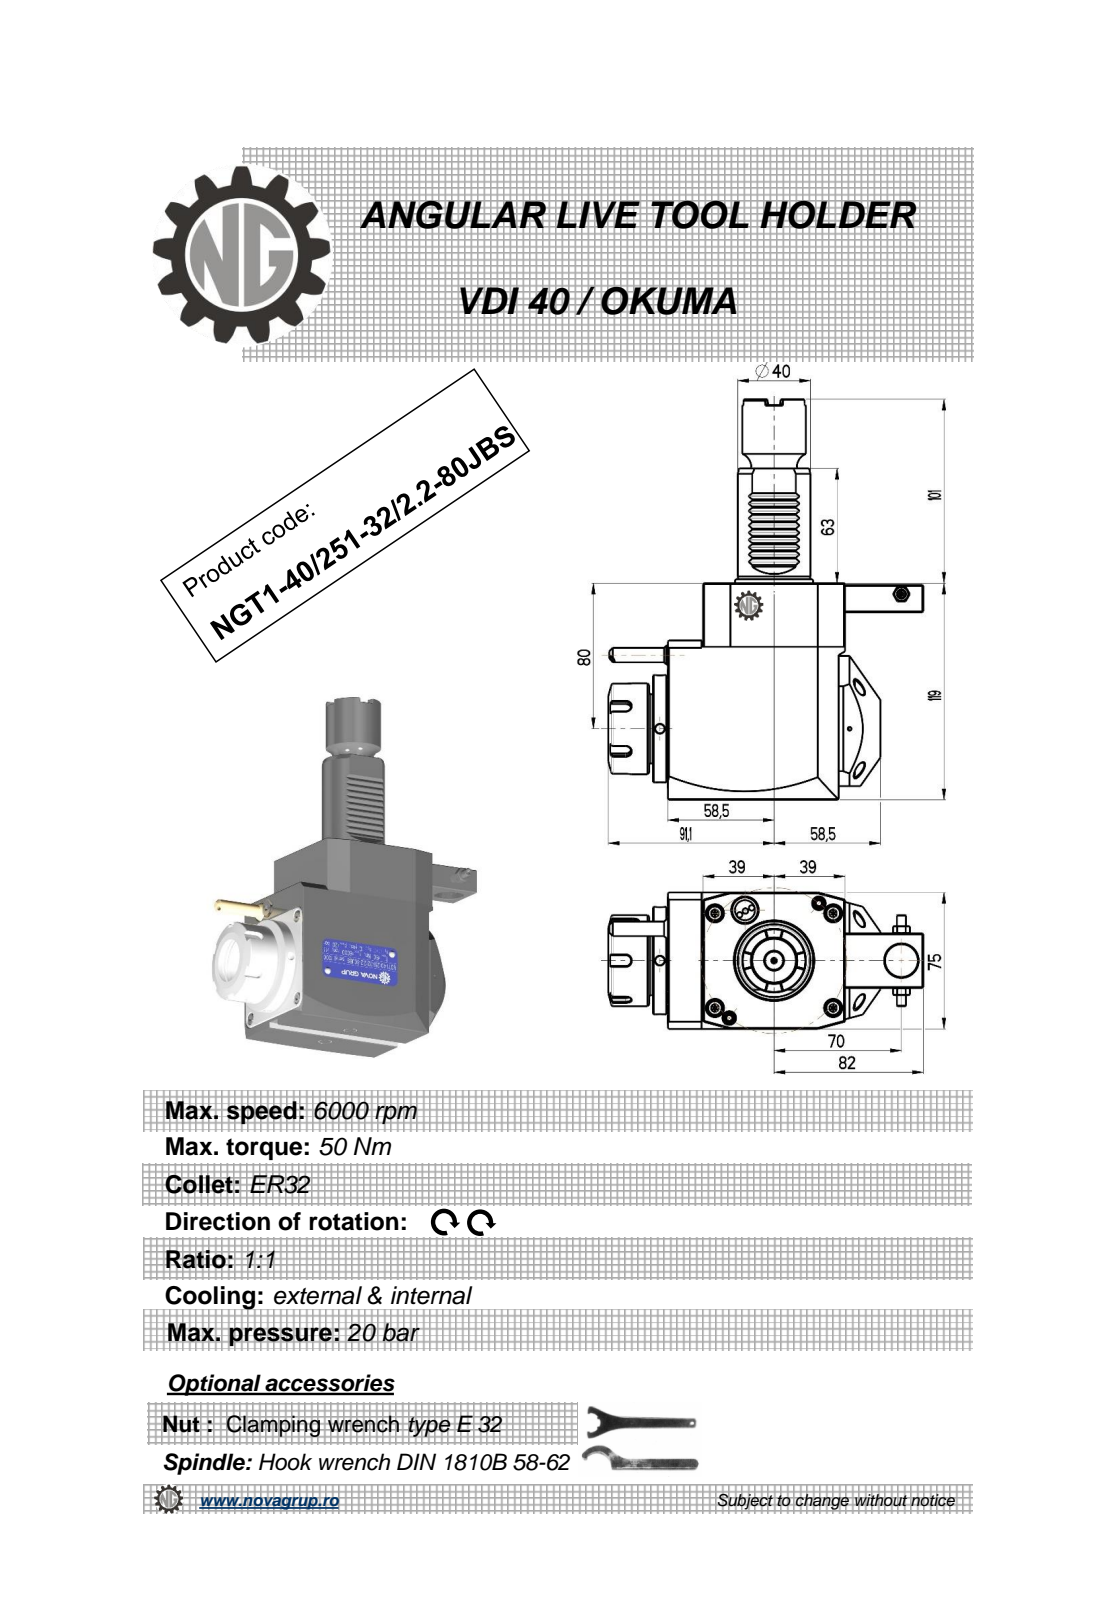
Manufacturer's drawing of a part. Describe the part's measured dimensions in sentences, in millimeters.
The part is named "NGT1_40_251_32_2_2_80JBS". Its 3-D file was written by "PRO/ENGINEER BY PARAMETRIC TECHNOLOGY CORPORATION, 2010280 (CONFIG_CONTROL_DESIGN)". It is 1 solid with 495 faces: 224 planar, 98 cylindrical and 173 other. Overall it measures 220 by 173.1 by 75 millimeters. Its volume is 1 041 000 cubic millimeters and its surface area 84 947 square millimeters. Round holes: 3 of diameter 5, 1 of diameter 3, 1 of diameter 4.2, 1 of diameter 9.5, 1 of diameter 18, 1 of diameter 25, 1 of diameter 27. Round bosses or shafts: 1 of diameter 59, 1 of diameter 50, 1 of diameter 47, 1 of diameter 41, 1 of diameter 40, 1 of diameter 35, 1 of diameter 10, 1 of diameter 8.96. Partial cylindrical surfaces (rounded edges, fillets, slot ends): 12 of radius 0.26, 10 of radius 0.3, 6 of radius 0.2, 5 of radius 3, 3 of radius 6, 2 of radius 5.8, 2 of radius 600, 1 of radius 0.5. The main face-to-face distances are 75, 119, 19.5, 97.5, 78, 3.5, 1, 19.3, 97.3, 20. The hole center spacings are 36.47, 44.12, 62.75, 70, 72.5, 132.75, 151.98.
